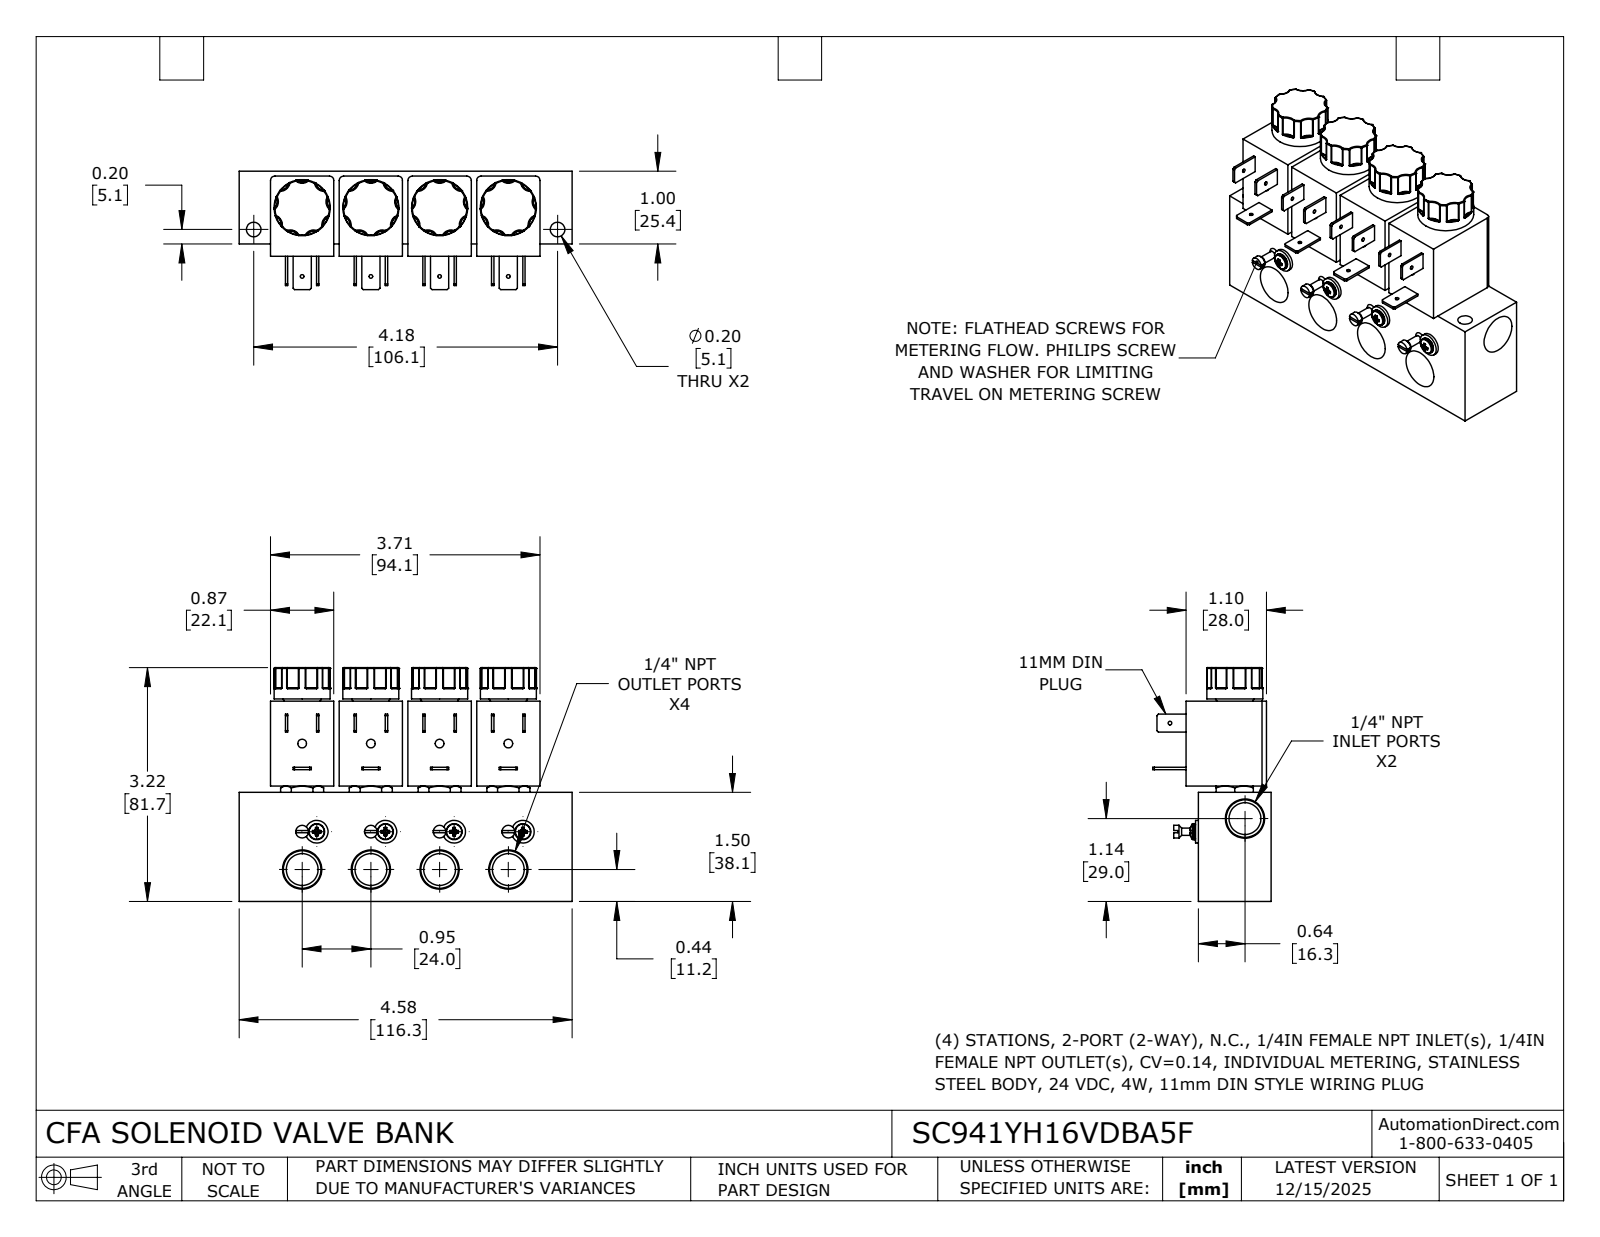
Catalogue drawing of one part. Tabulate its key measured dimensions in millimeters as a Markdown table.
| quantity | value |
| --- | --- |
| part name | SC941YH16VDBA5F |
| STEP written by | SolidWorks 2024 (CONFIG_CONTROL_DESIGN) |
| units | millimeters |
| bodies | 1 solid, 1098 faces (284 planar, 260 cylindrical, 554 other) |
| overall size | 116.3 × 81.7 × 41.3 |
| volume | 188 300 mm³ |
| surface area | 44 010 mm² |
| round holes (diameter × count) | 1.3 × 5, 11.1 × 5, 3 × 4, 5.1 × 2 |
| round bosses / shafts (diameter × count) | 19.6 × 4, 7.9 × 4, 5.6 × 4, 4.4 × 4, 2.5 × 4 |
| partial cylindrical surfaces (radius × count) | 0.3 × 72, 3.4 × 28, 1.5 × 8, 3.4 × 8 |
| main face-to-face distances | 25.4, 24, 29.7, 4.3, 48, 22.1, 46.1, 38.1, 1.7, 23.7 |
| hole center spacings | 24, 44, 50.1, 24, 48, 48, 72, 50.1 |
